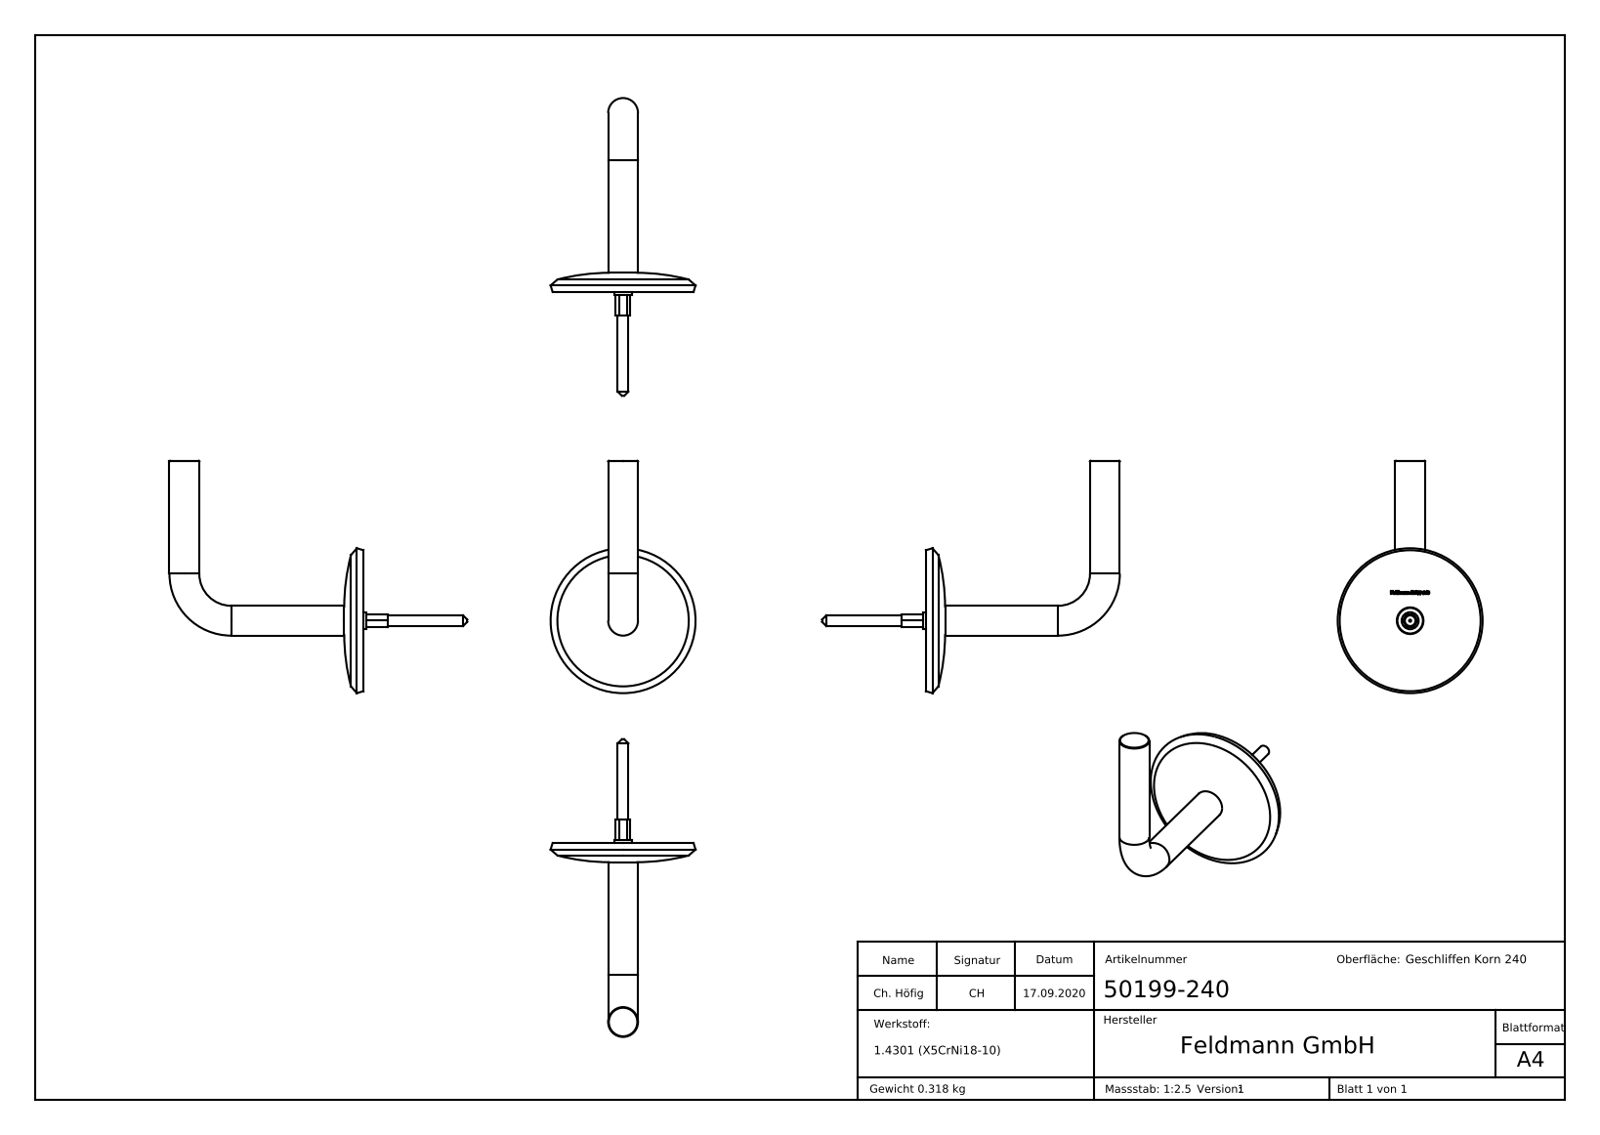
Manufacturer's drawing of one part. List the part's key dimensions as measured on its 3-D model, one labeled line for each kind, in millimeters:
Part name (STEP PRODUCT): 50199-240 Teil2; 50199-240 Teil3; 50199-240 Teil1; 50199-240 Teil3_50199-240 Teil 4 (+3 more)
STEP written by: SolidWorks 2018 (CONFIG_CONTROL_DESIGN)
Units: millimetres
Bodies: 3 solids, 262 faces (107 planar, 12 cylindrical, 143 other)
Overall size (bounding box): 139.76 × 109 × 68
Volume: 40 313 mm³ · Surface area: 16 630 mm²
Round holes (diameter × count): ⌀6.8 ×1, ⌀12.5 ×1
Round bosses / shafts (diameter × count): ⌀14 ×2, ⌀8 ×1, ⌀5 ×1
Main face-to-face distances: 6, 78, 72, 22.24, 10.26, 32.5, 10, 20.26, 42.5, 37.5
